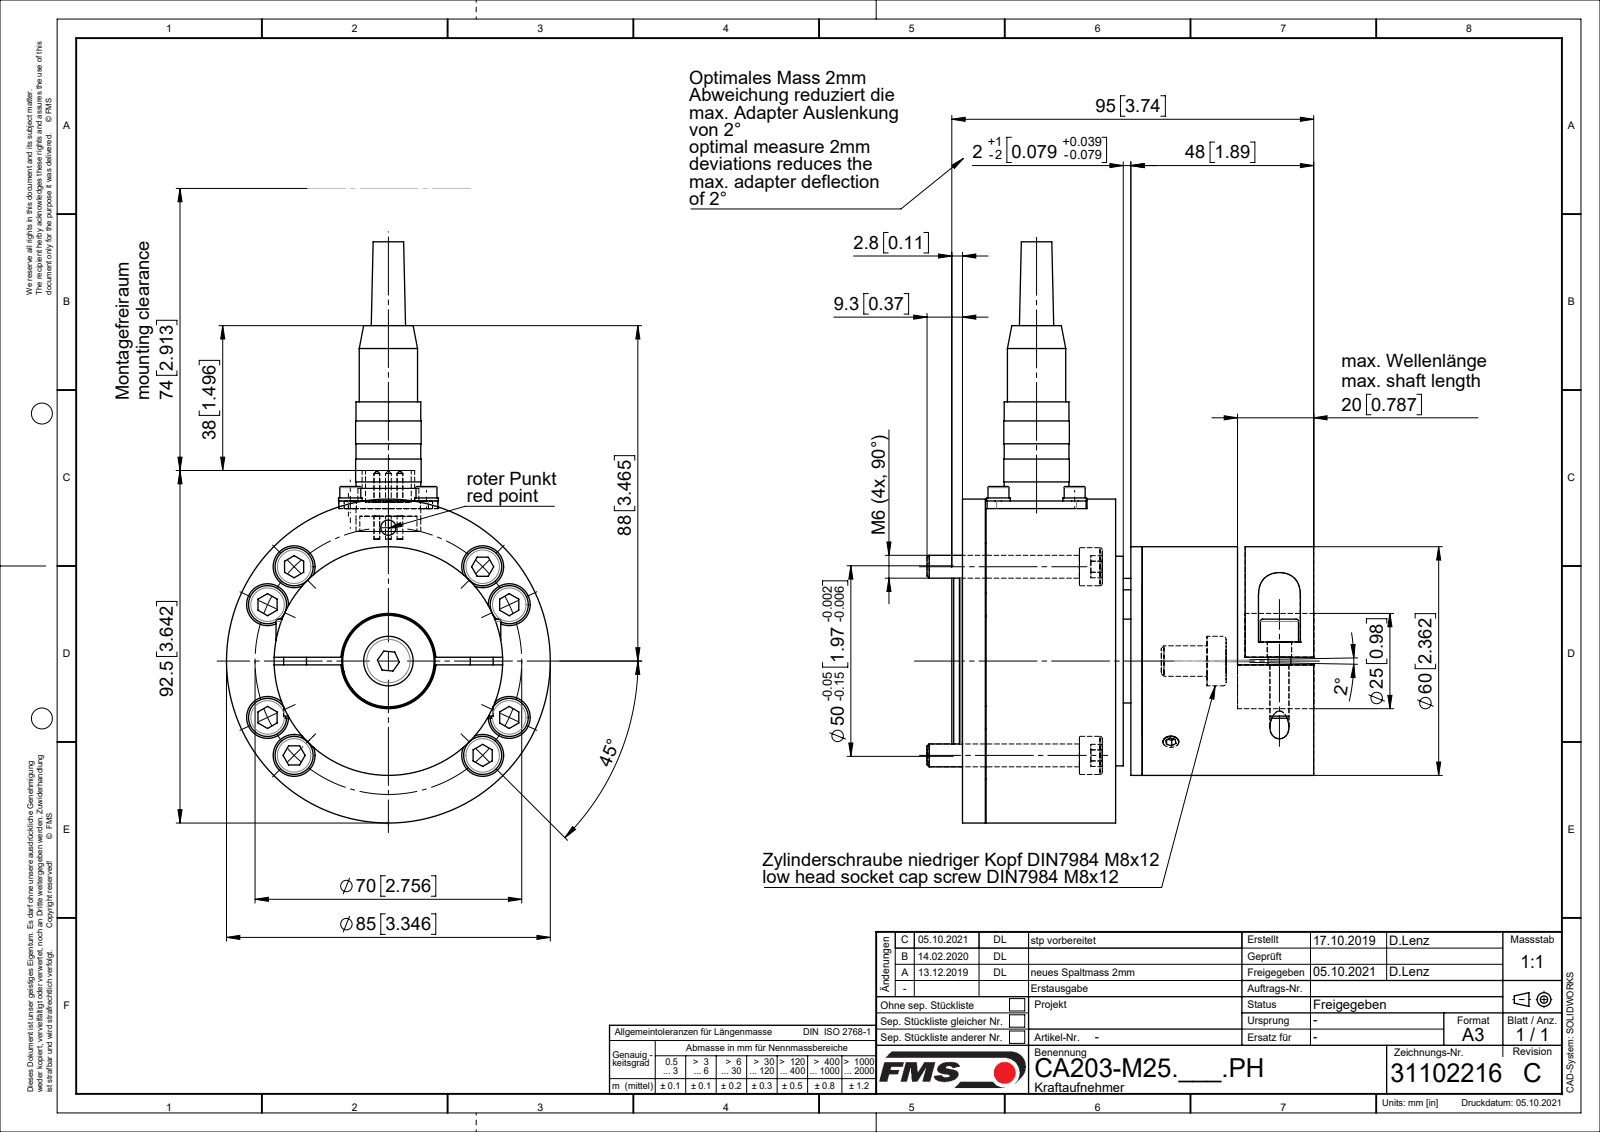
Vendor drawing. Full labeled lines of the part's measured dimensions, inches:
Part name (STEP PRODUCT): Zyl-Schr DIN912_M6x40; 070403-1_01; Senkniete_90°_d3x10; Federringe_DIN127A_M03 (+8 more)
STEP written by: SolidWorks 2018 (CONFIG_CONTROL_DESIGN)
Units: inches
Bodies: 44 solids, 821 faces (294 planar, 332 cylindrical, 195 other)
Overall size (bounding box): 6.004 × 3.996 × 3.346
Volume: 18.46 in³ · Surface area: 170.2 in²
Round holes (diameter × count): ⌀0.098 ×8, ⌀0.256 ×8, ⌀0.433 ×8, ⌀0.197 ×6, ⌀0.157 ×5, ⌀0.122 ×4, ⌀0.126 ×4, ⌀0.142 ×4, ⌀0.276 ×4, ⌀0.252 ×2, ⌀0.118 ×1, ⌀0.165 ×1
Round bosses / shafts (diameter × count): ⌀0.236 ×11, ⌀0.394 ×10, ⌀0.118 ×8, ⌀0.059 ×5, ⌀0.244 ×4, ⌀0.224 ×4, ⌀0.217 ×4, ⌀3.346 ×1
Partial cylindrical surfaces — rounded edges, fillets, slot ends (radius × count): R0.098 ×4, R0.197 ×2, R0.217 ×2
Main face-to-face distances: 0.079, 1.614, 1.181, 0.236, 1.772, 0.394, 1.969, 1.339, 0.118, 0.472
Hole centre spacings: 1.378, 0.787, 0.976, 0.992, 1.291, 2.013, 2.223, 1.113
